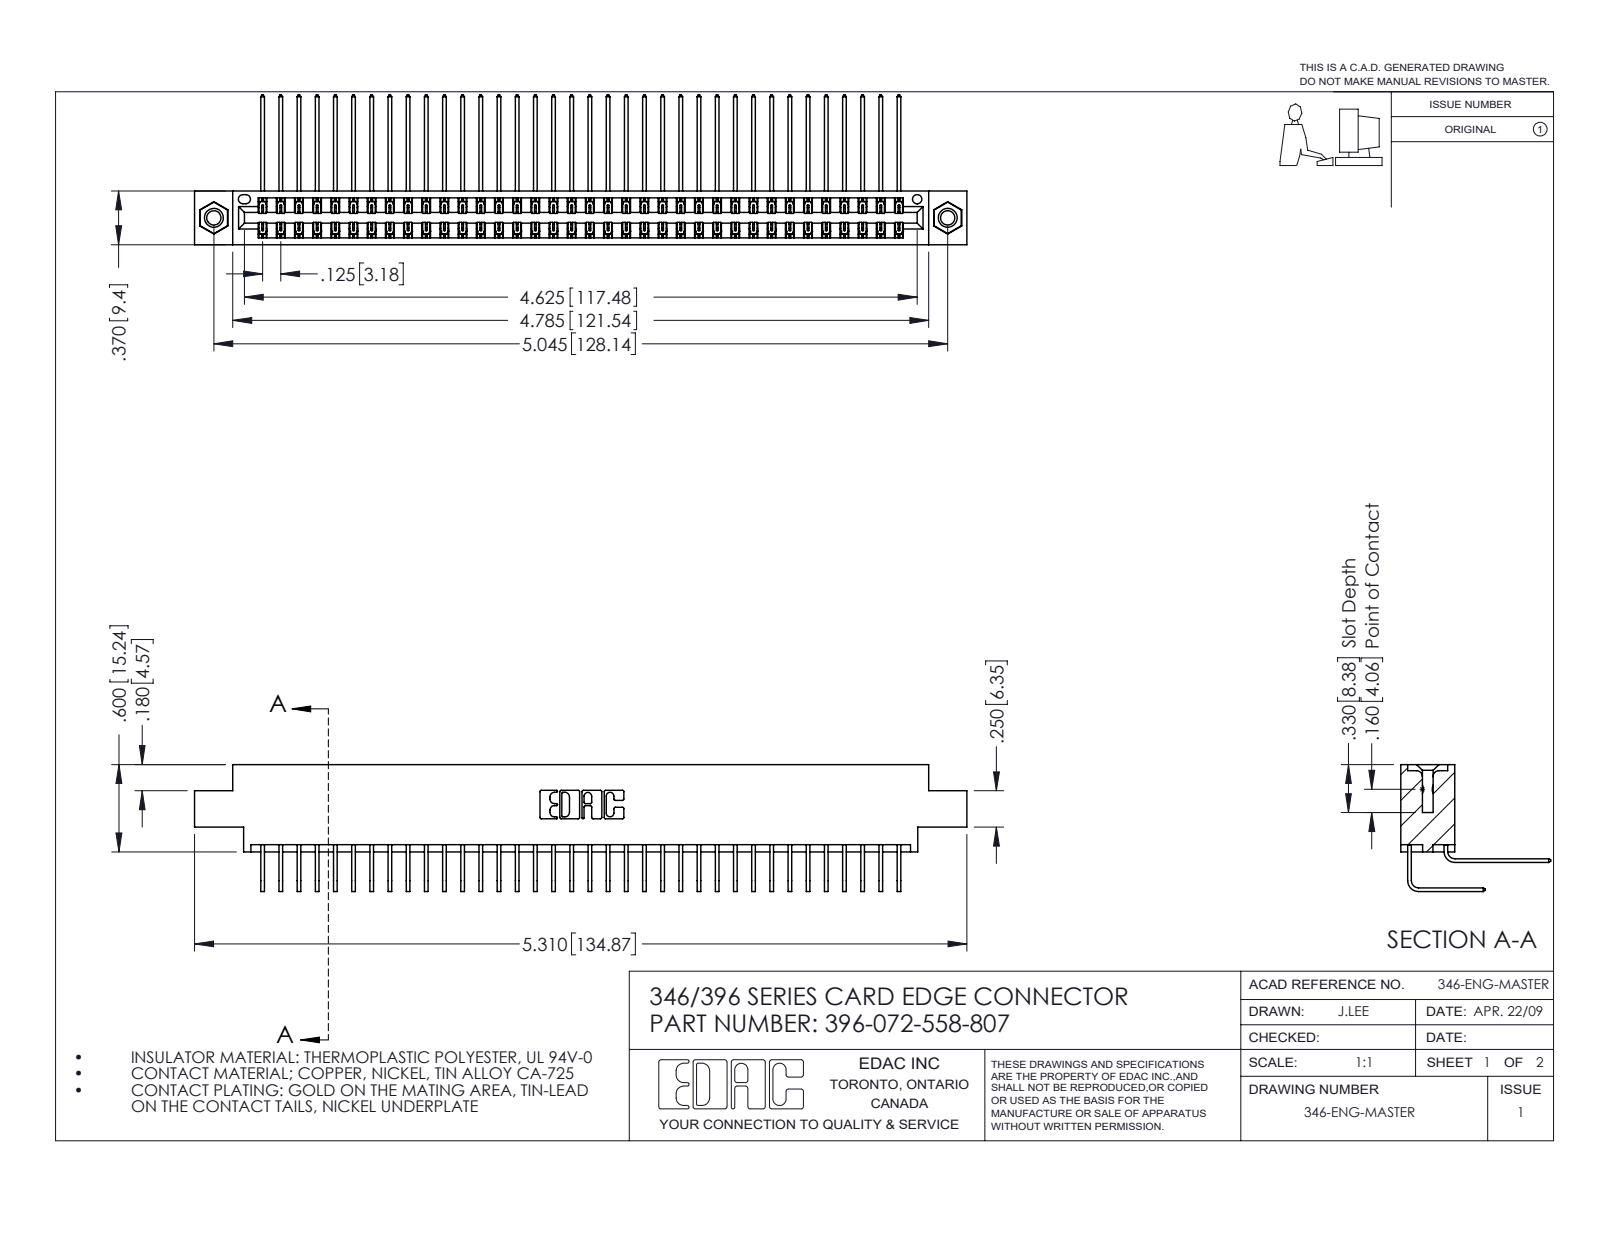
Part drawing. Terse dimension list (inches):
name: 345-292-001_558 559 Tail - 1; 346 Part_0.170 Offset - 0.156 Dia-TI; 345-250-001_345-250-005-103; 345-292-001_558 Tail - 2 (+1 more)
written by: SolidWorks 2016 (CONFIG_CONTROL_DESIGN)
unit: in
bodies: 75 solids, 4074 faces (2776 planar, 1282 cylindrical, 16 other)
size: 5.31 × 1.03 × 0.873
volume: 0.815 in³; area: 31.72 in²
holes: 2× ⌀0.098, 2× ⌀0.125, 2× ⌀0.156, 1× ⌀0.064
bosses: 2× ⌀0.155
rounds: 108× R0.006, 22× R0.01, 6× R0.007, 6× R0.031, 3× R0.026, 2× R0.014, 2× R0.022, 2× R0.024
face distances: 0.322, 0.048, 0.025, 0.37, 0.25, 0.298, 0.072, 0.275, 0.222, 0.148
hole spacings: 0.246, 4.836, 5.045
